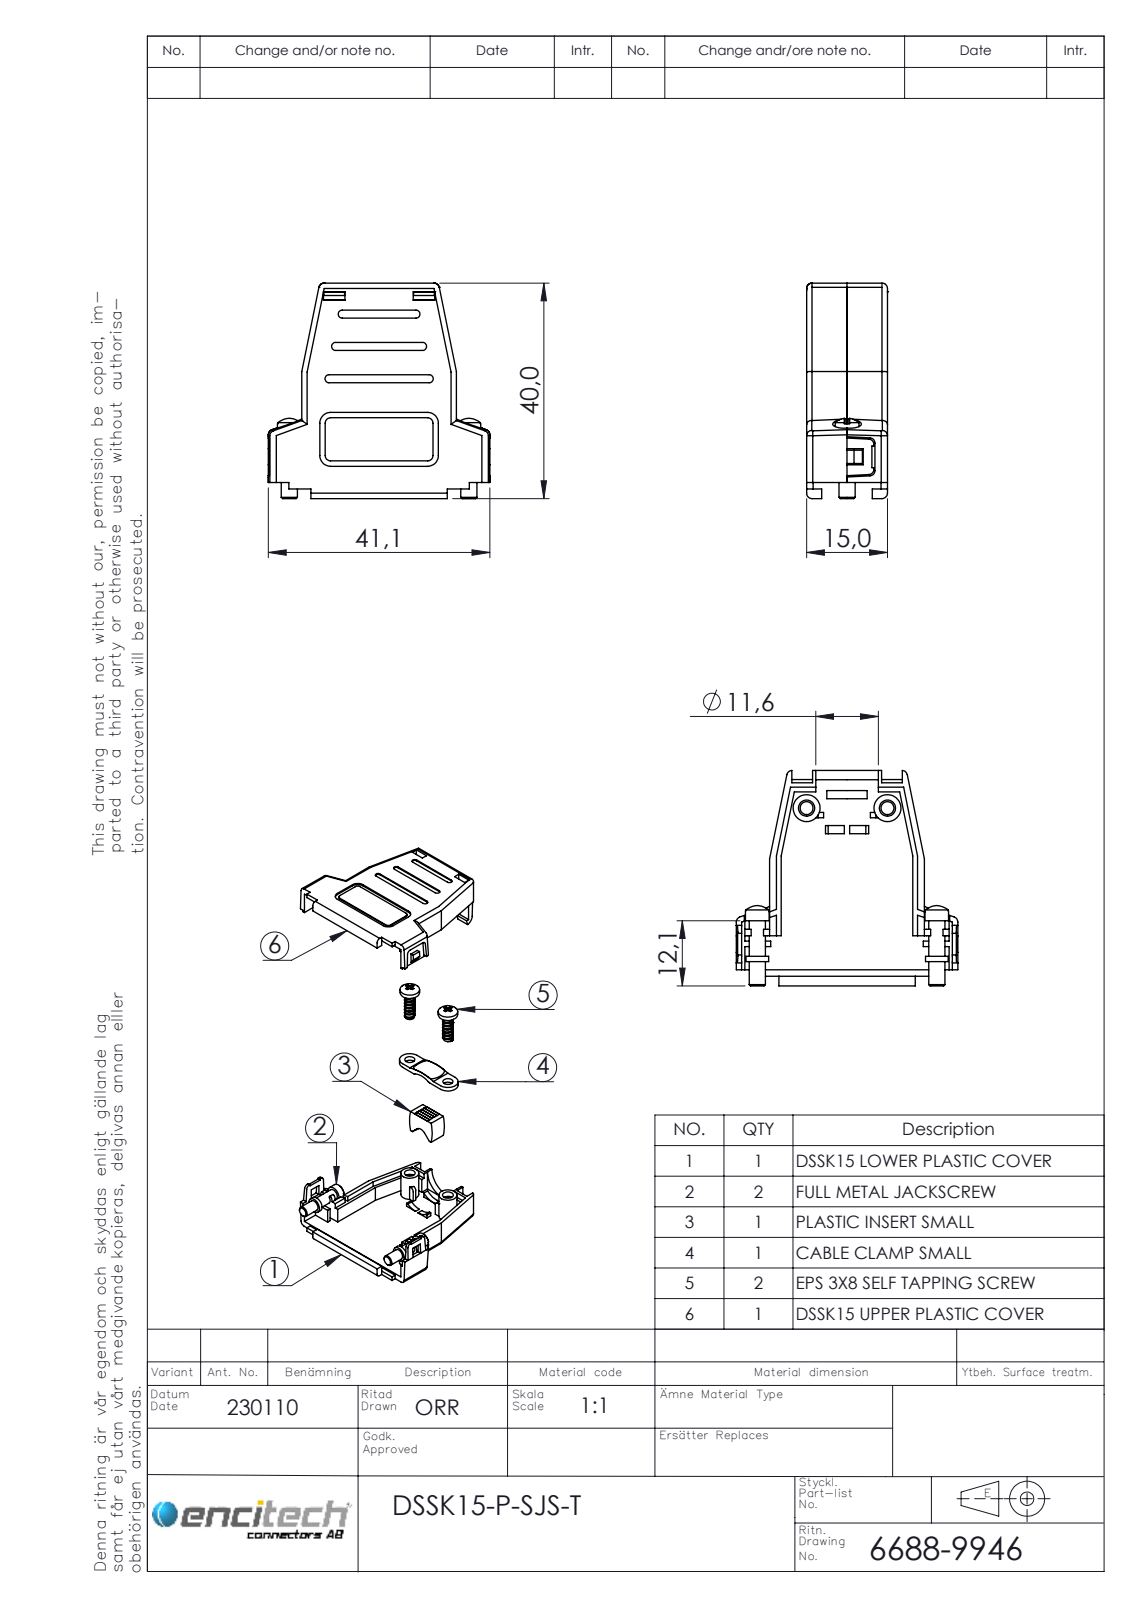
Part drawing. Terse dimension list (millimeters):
name: 6855-0109-01; 6811-0162-13 Part 1; 6826-0133-04; 6688-9946 (+3 more)
written by: SolidWorks 2021 (AUTOMOTIVE_DESIGN)
unit: mm
bodies: 10 solids, 872 faces (550 planar, 259 cylindrical, 63 other)
size: 41.1 × 40 × 15
volume: 7 141 mm³; area: 10 608 mm²
holes: 2× ⌀2.4, 2× ⌀2.8, 2× ⌀3, 1× ⌀0.75, 1× ⌀0.9, 1× ⌀1.25, 1× ⌀2.5, 1× ⌀3.5, 1× ⌀11.6
bosses: 2× ⌀5.45, 2× ⌀5, 2× ⌀4.4, 2× ⌀4.2, 2× ⌀3, 2× ⌀2.46
rounds: 32× R1, 24× R0.25, 20× R0.5, 16× R0.12, 6× R0.75, 6× R2, 4× R0.4, 4× R1.2
face distances: 1.7, 13.3, 11.6, 15, 7.5, 5.8, 7.3, 1.5, 1.2, 2.15
hole spacings: 7.54, 7.8, 8.2, 9.27, 9.3, 11.75, 12.73, 15
